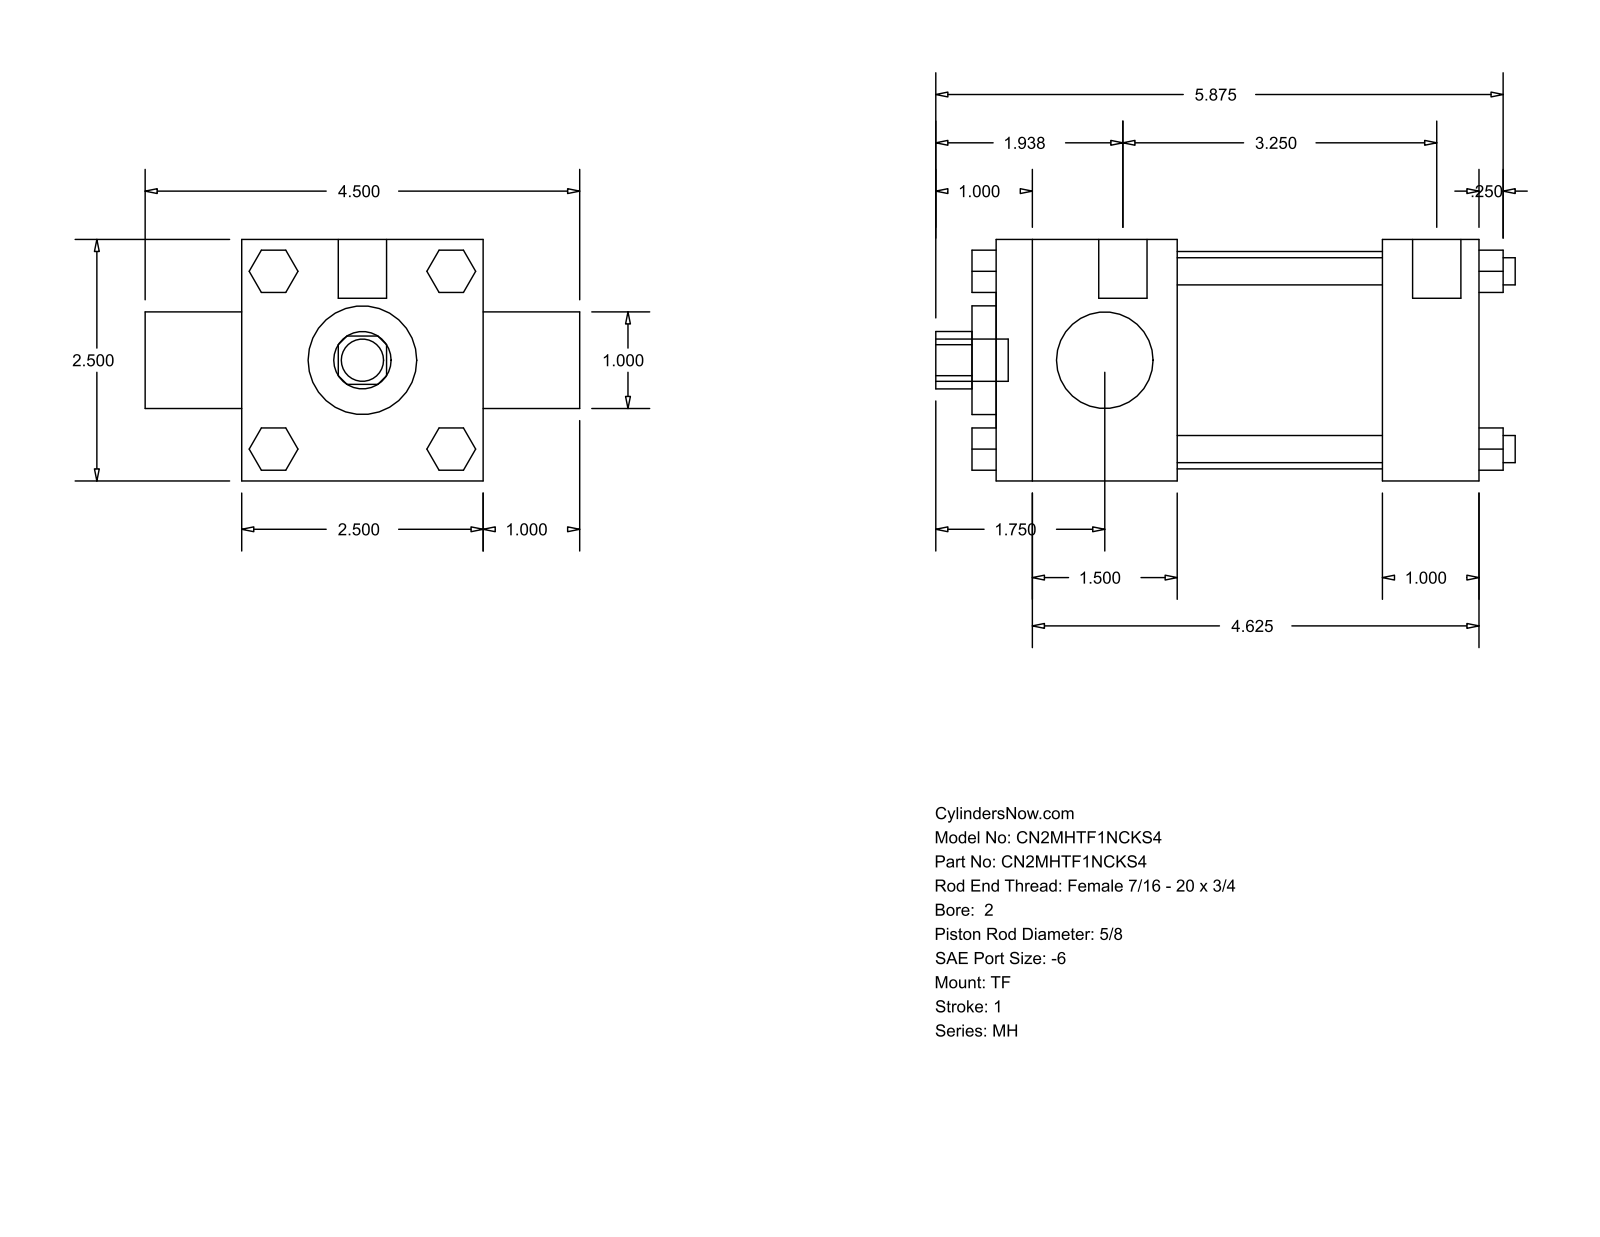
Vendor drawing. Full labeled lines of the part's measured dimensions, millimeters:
Part name (STEP PRODUCT): MH_TF__0200_0.625
STEP written by: GSSL Pune (CONFIG_CONTROL_DESIGN)
Units: millimetres
Bodies: 0 solids, 120 faces (92 planar, 28 cylindrical, 0 other)
Overall size (bounding box): 152.4 × 114.3 × 63.5
Round holes (diameter × count): ⌀15.88 ×1, ⌀25.4 ×1, ⌀28.57 ×1, ⌀57.15 ×1
Round bosses / shafts (diameter × count): ⌀7.14 ×4, ⌀5.56 ×3, ⌀12.7 ×2, ⌀11.11 ×1
Partial cylindrical surfaces — rounded edges, fillets, slot ends (radius × count): R7.54 ×1
Main face-to-face distances: 63.5, 127, 53.97, 47.62, 101.59, 79.38, 25.41, 25.4, 88.9, 133.35
